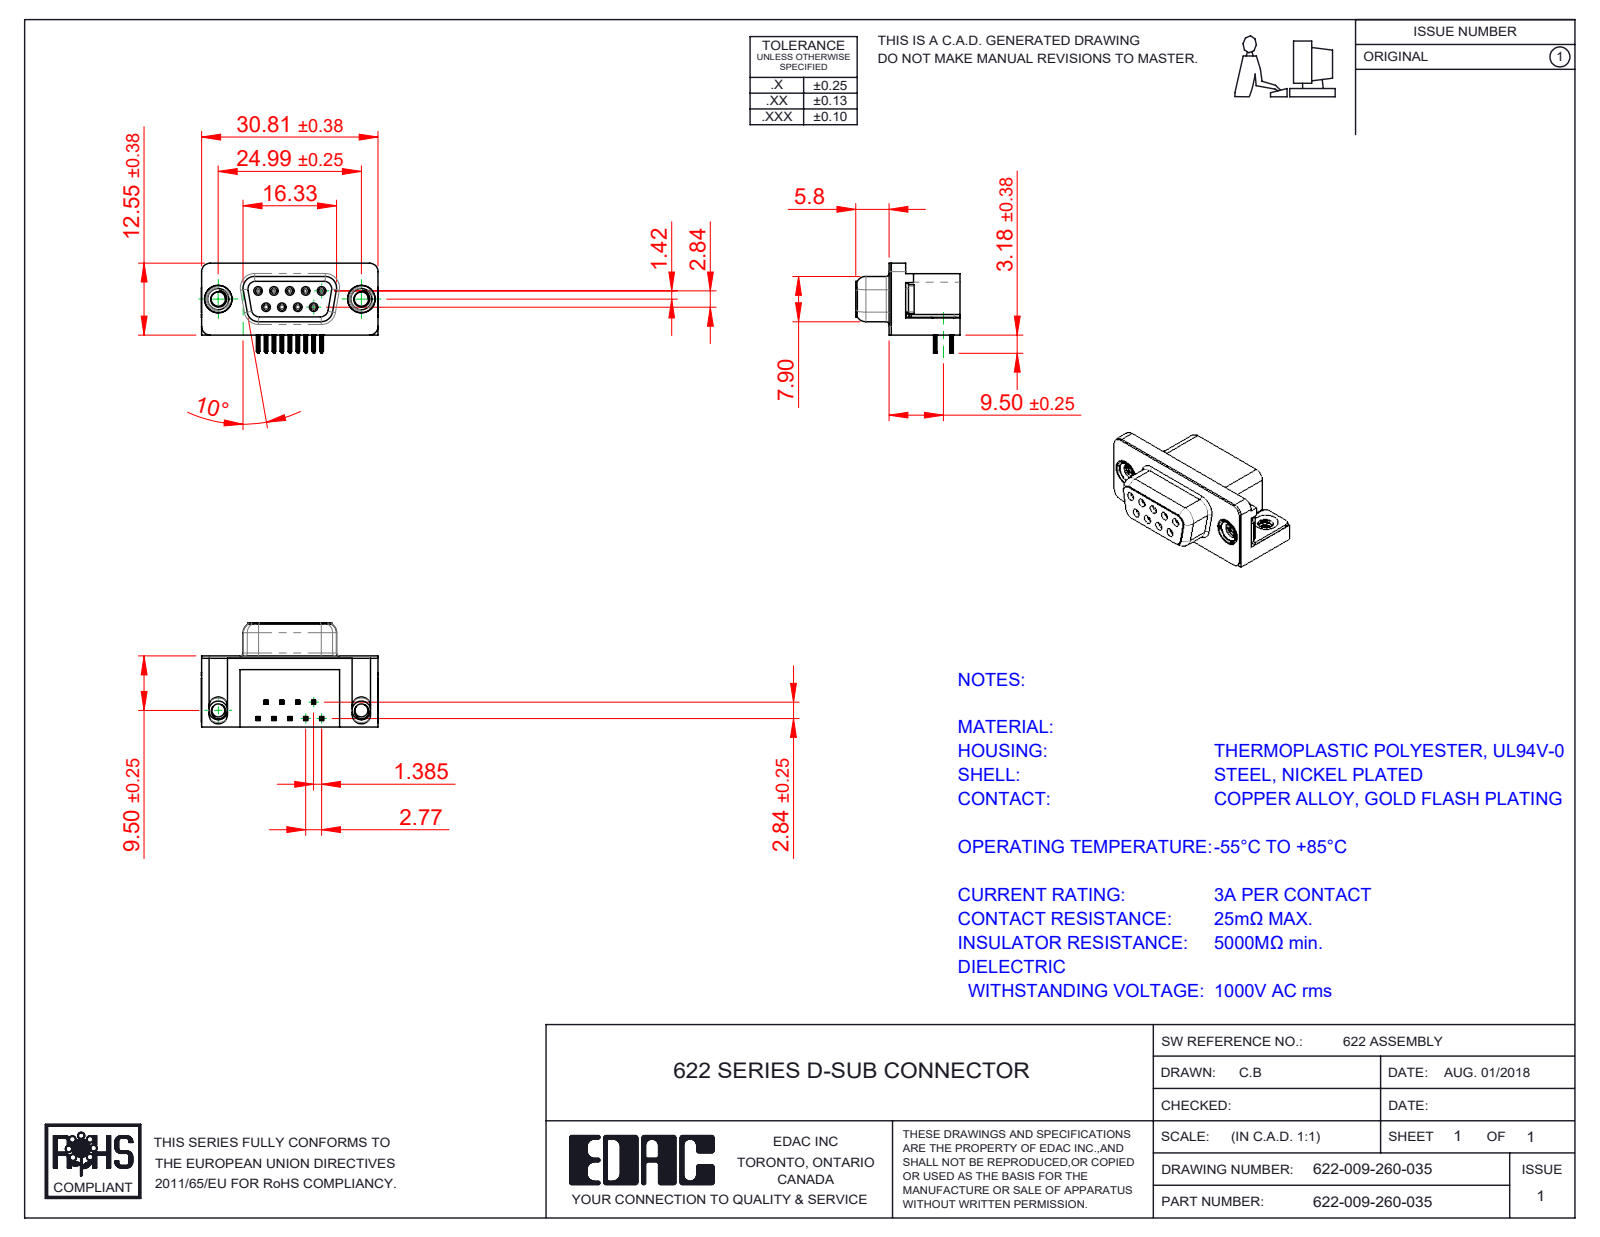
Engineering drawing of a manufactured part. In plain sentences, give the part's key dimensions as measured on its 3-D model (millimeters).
The part is named "622-009-260-035; 622 Shell_9 Socket; 622 Socket Bottom; 622 M3 Threaded Rivet (+3 more)". Its 3-D file was written by "SolidWorks 2016 (CONFIG_CONTROL_DESIGN)". It is 15 solids with 1612 faces: 716 planar, 428 cylindrical and 468 other. Overall it measures 30.89 by 18.2 by 16.25 millimeters. Its volume is 3 720 cubic millimeters and its surface area 5 082 square millimeters. Round holes: 9 of diameter 0.8, 9 of diameter 0.9, 2 of diameter 2.5, 2 of diameter 4, 2 of diameter 4.8, 2 of diameter 5. Round bosses or shafts: 9 of diameter 1.2, 2 of diameter 4.9, 2 of diameter 4.75, 2 of diameter 3.9. Partial cylindrical surfaces (rounded edges, fillets, slot ends): 72 of radius 0.1, 36 of radius 0.15, 18 of radius 0.35, 18 of radius 1, 10 of radius 0.5, 9 of radius 0.34, 8 of radius 0.25, 8 of radius 1.35. The main face-to-face distances are 0.4, 12, 12.4, 0.35, 2.9, 2.5, 6.2, 10.34, 0.5, 9.5. The hole center spacings are 3.16, 2.77, 5.54, 5.03, 5.04, 8.31, 7.48, 7.49.
